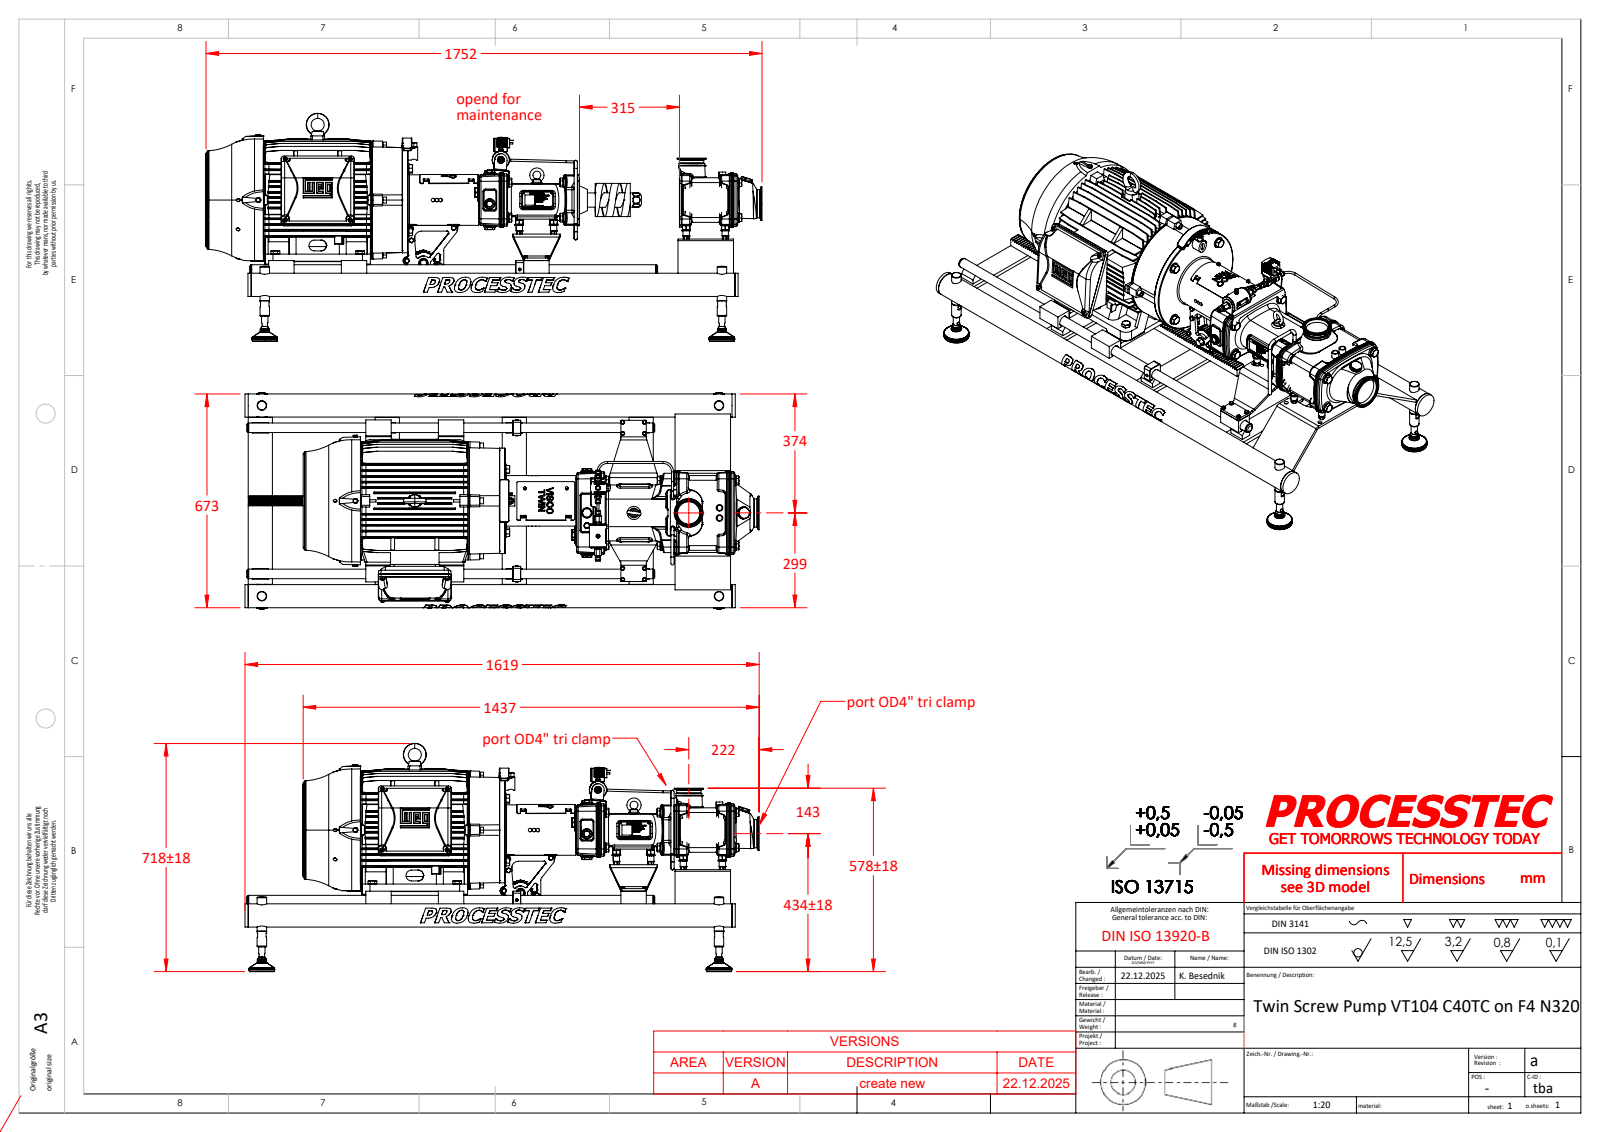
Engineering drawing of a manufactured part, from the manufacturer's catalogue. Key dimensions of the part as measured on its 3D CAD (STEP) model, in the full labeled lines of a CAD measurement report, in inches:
Part name (STEP PRODUCT): 001334; 001405; 001090_ISO 2338 - 8 h8 x 20 - A1; 001382 (+8 more)
STEP written by: SolidWorks 2023 (AUTOMOTIVE_DESIGN)
Units: inches
Bodies: 199 solids, 18463 faces (7425 planar, 3857 cylindrical, 7181 other)
Overall size (bounding box): 63.76 × 28.298 × 26.791
Volume: 5 776 in³ · Surface area: 12 650 in²
Round holes (diameter × count): ⌀0.335 ×22, ⌀0.197 ×21, ⌀0.315 ×15, ⌀0.551 ×13, ⌀0.268 ×12, ⌀0.512 ×12, ⌀0.433 ×11, ⌀0.413 ×9, ⌀0.689 ×9, ⌀0.252 ×8, ⌀0.354 ×8, ⌀0.398 ×8
Round bosses / shafts (diameter × count): ⌀0.394 ×34, ⌀0.945 ×24, ⌀0.236 ×20, ⌀0.315 ×15, ⌀0.787 ×12, ⌀0.728 ×12, ⌀0.669 ×12, ⌀0.591 ×12
Partial cylindrical surfaces — rounded edges, fillets, slot ends (radius × count): R0.117 ×188, R0.059 ×79, R0.197 ×70, R0.236 ×54, R0.019 ×50, R0.079 ×48, R0.315 ×40, R0.157 ×25
Main face-to-face distances: 13.476, 0.5, 0.315, 4.016, 17.492, 0.079, 0.667, 29.579, 16.102, 12.087
Hole centre spacings: 18.166, 2.165, 15.748, 5.5, 7.612, 9.055, 32.772, 6.411
